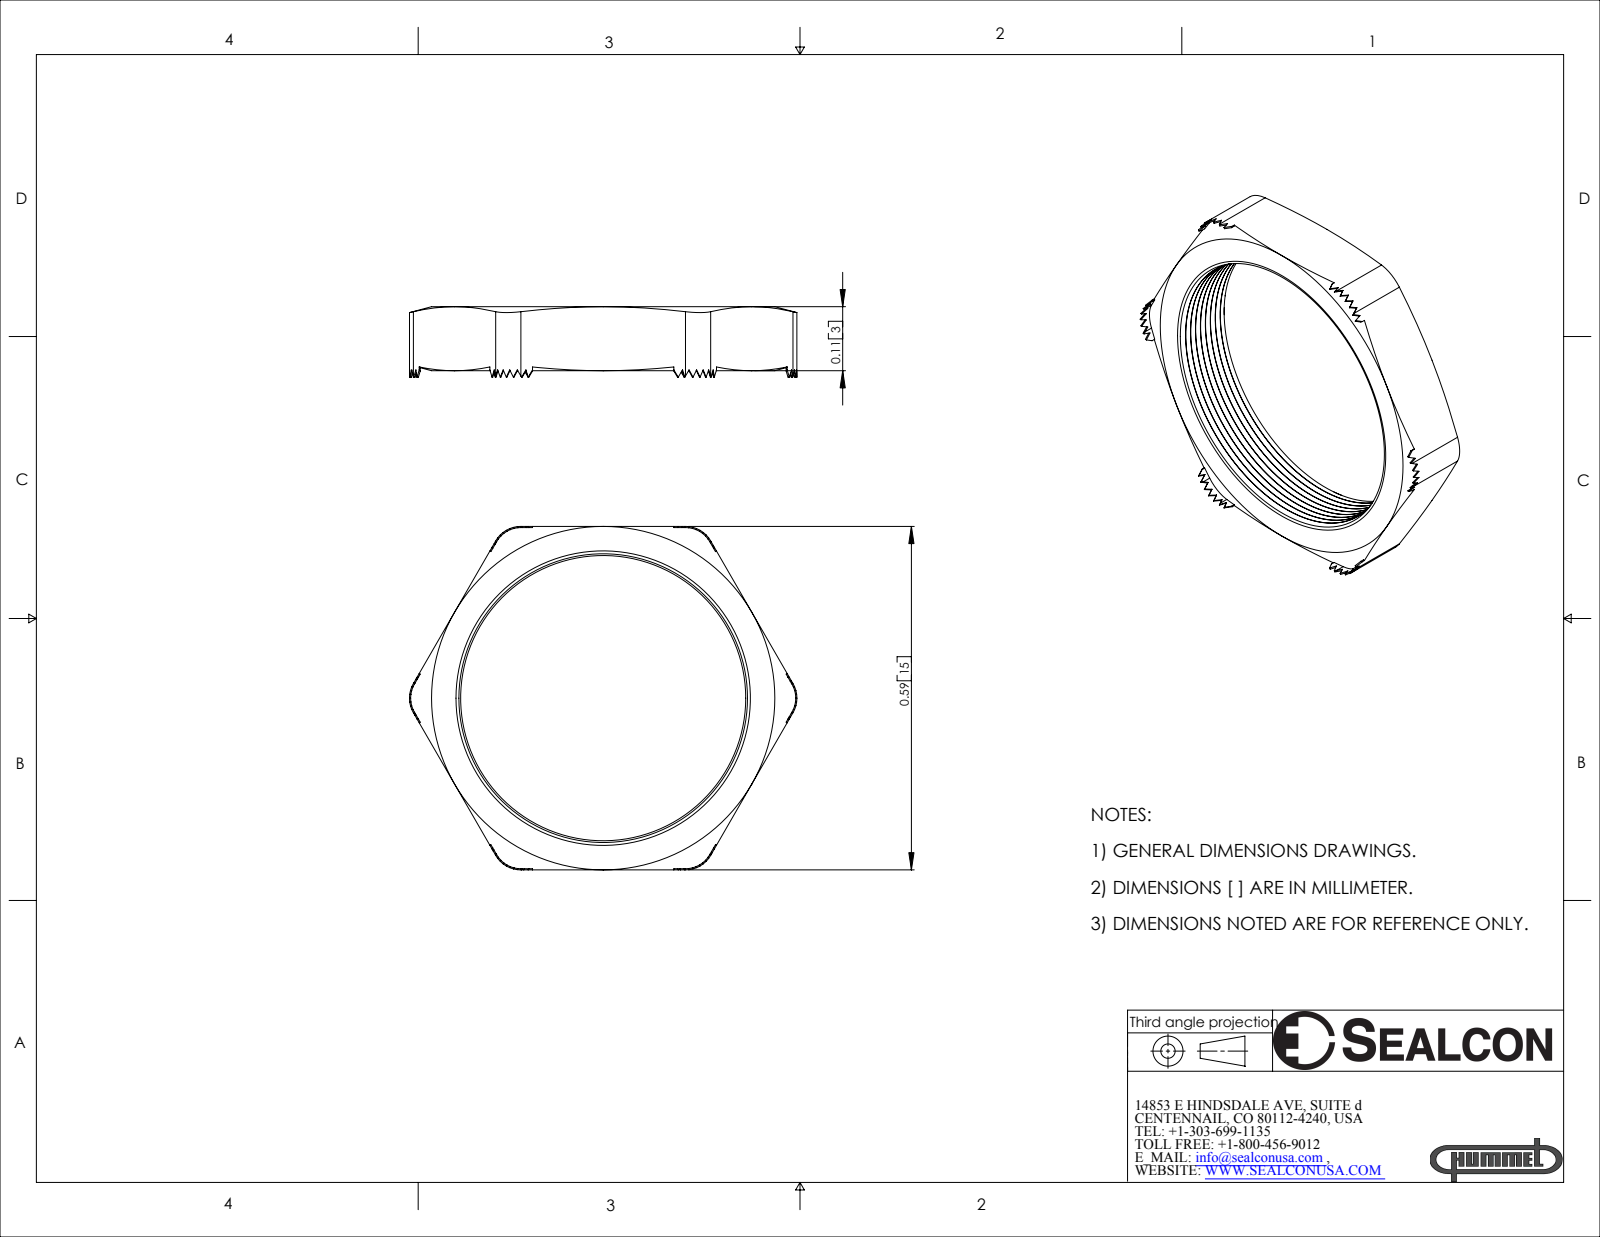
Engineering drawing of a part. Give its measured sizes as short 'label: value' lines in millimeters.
name: NP-07-BE
written by: SolidWorks 2007 (CONFIG_CONTROL_DESIGN)
unit: mm
bodies: 1 solid, 200 faces (116 planar, 30 cylindrical, 54 other)
size: 16.9 × 15 × 3.1
volume: 180 mm³; area: 495 mm²
holes: 1× ⌀12.4
rounds: 6× R1.2, 6× R1.3
face distances: 15, 2.8, 14.9, 14.9, 0.6, 0.9, 0.6, 1.1, 0.8, 1.4
